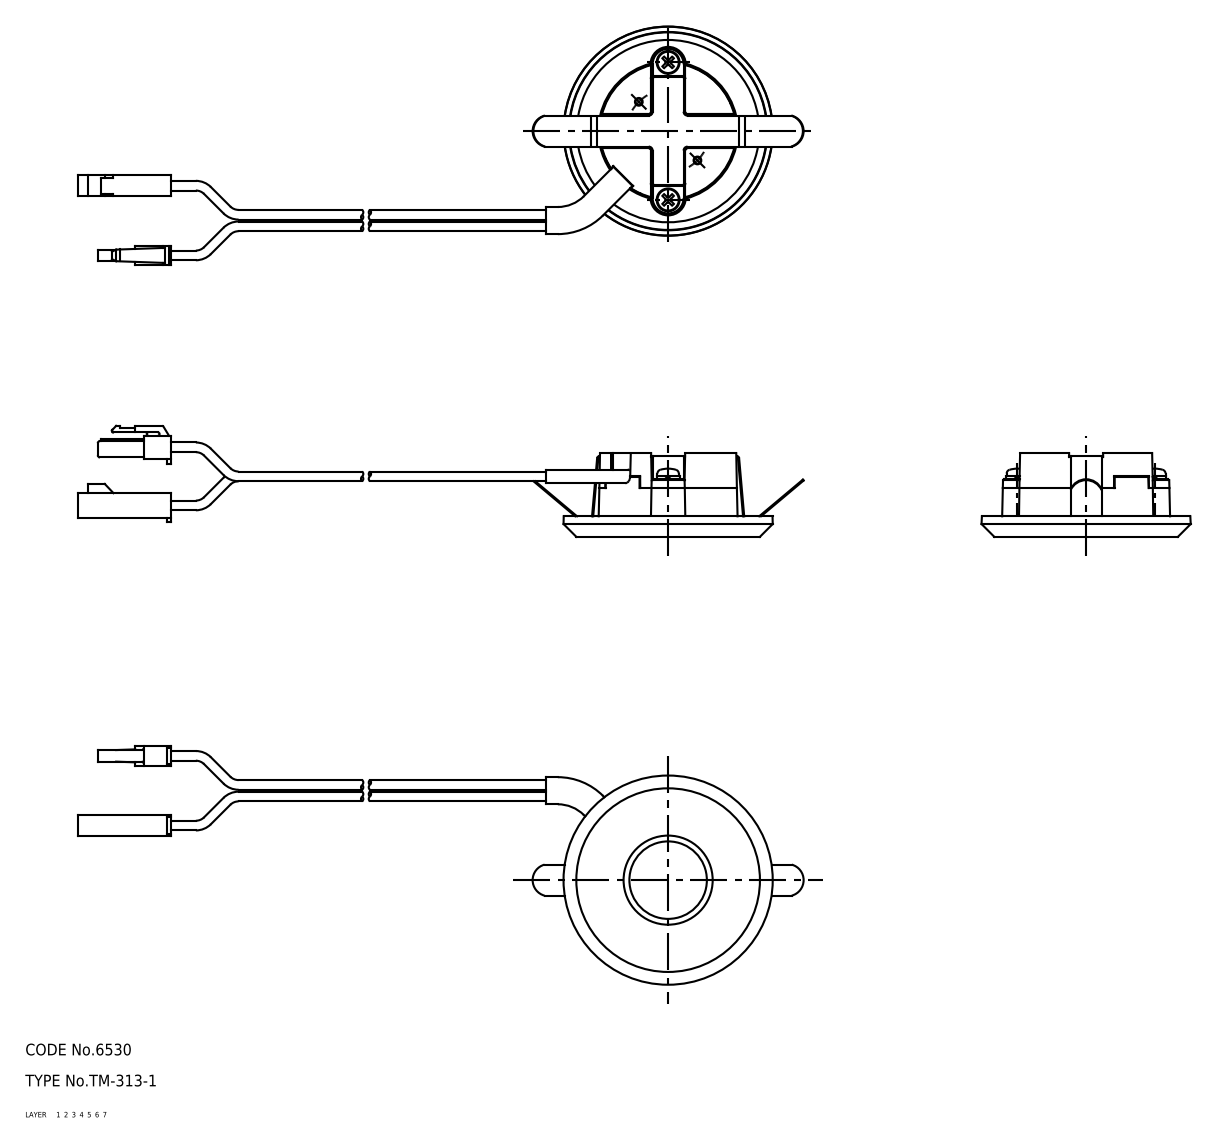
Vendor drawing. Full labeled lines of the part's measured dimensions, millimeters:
Part name (STEP PRODUCT): 67123948; 67123961; 67123974; 67123987 (+4 more)
STEP written by: CADfix (AUTOMOTIVE_DESIGN)
Units: millimetres
Bodies: 8 solids, 315 faces (0 planar, 0 cylindrical, 315 other)
Overall size (bounding box): 187.34 × 54.07 × 28.64
Volume: 23 177 mm³ · Surface area: 16 576 mm²
